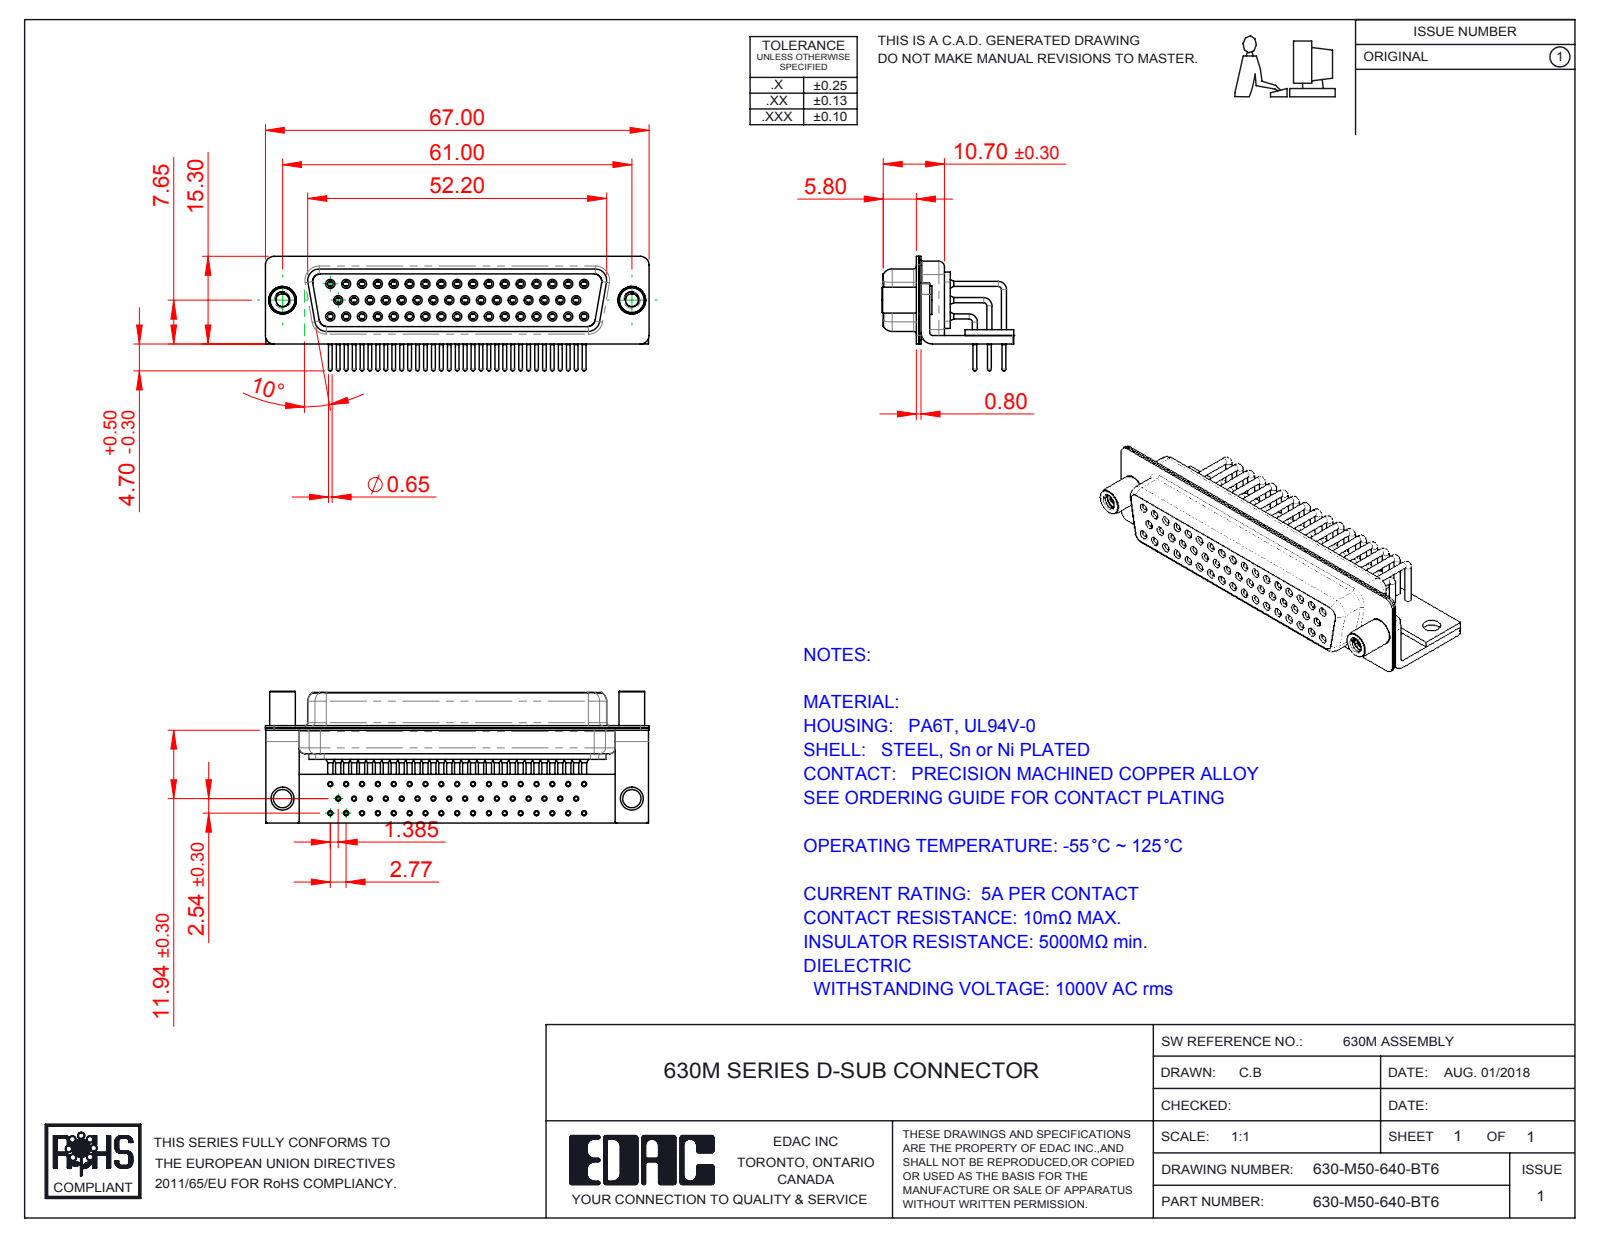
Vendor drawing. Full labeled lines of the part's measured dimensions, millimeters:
Part name (STEP PRODUCT): 630M Shell Rear_50 Contacts; 630M Contact Row 1_50 Contacts; 630M Contact Row 2_50 Contacts; 630M Contact Row 3 (+6 more)
STEP written by: SolidWorks 2016 (CONFIG_CONTROL_DESIGN)
Units: millimetres
Bodies: 58 solids, 3129 faces (845 planar, 1451 cylindrical, 833 other)
Overall size (bounding box): 67 × 23 × 20
Volume: 7 991 mm³ · Surface area: 18 922 mm²
Round holes (diameter × count): ⌀0.9 ×50, ⌀1 ×50, ⌀1.1 ×50, ⌀1.7 ×50, ⌀1.8 ×50, ⌀2 ×50, ⌀2.26 ×2, ⌀3.2 ×2, ⌀4 ×2, ⌀4.8 ×2
Round bosses / shafts (diameter × count): ⌀0.9 ×59, ⌀1.6 ×50, ⌀1.5 ×50, ⌀0.65 ×50, ⌀5 ×2, ⌀4.9 ×2, ⌀4.5 ×2
Partial cylindrical surfaces — rounded edges, fillets, slot ends (radius × count): R0.25 ×16, R1.5 ×16, R2 ×13, R1.35 ×8, R1.6 ×8, R0.5 ×5, R0.6 ×4, R0.65 ×4
Main face-to-face distances: 0.4, 1, 2.2, 0.85, 1.35, 11.85, 12.25, 5.8, 0.8, 5.9
Hole centre spacings: 2.77, 5.54, 8.31, 11.08, 13.85, 16.62, 3.16, 19.39
